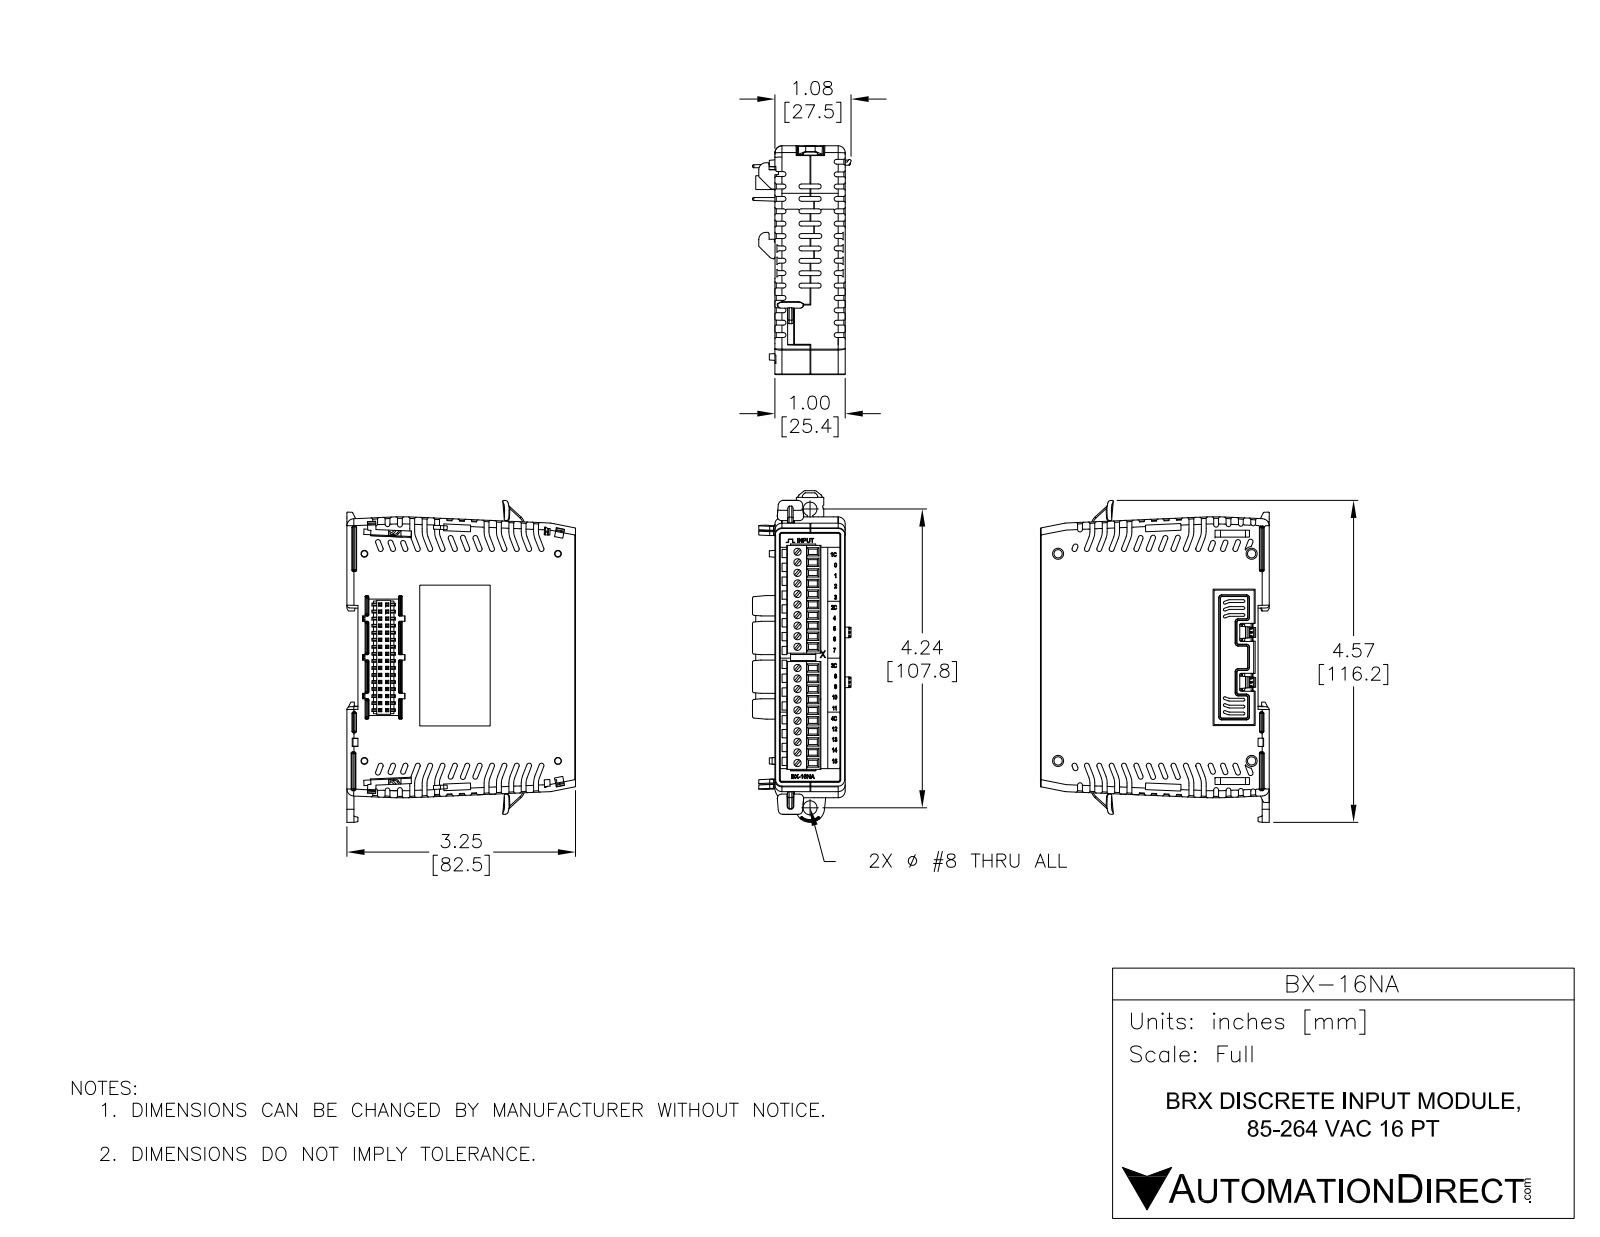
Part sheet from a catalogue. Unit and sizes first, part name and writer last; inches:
Units: inches
Overall size (bounding box): 4.586 × 3.25 × 1.402
Round holes (diameter × count): ⌀0.047 ×2, ⌀0.065 ×2, ⌀0.118 ×2, ⌀0.118 ×2, ⌀0.199 ×1
Round bosses / shafts (diameter × count): ⌀0.062 ×2, ⌀0.059 ×2
Partial cylindrical surfaces — rounded edges, fillets, slot ends (radius × count): R0.005 ×102, R0.008 ×101, R0.01 ×47, R0.02 ×34, R0.005 ×24, R0.062 ×20, R0.117 ×14, R0.039 ×13
Main face-to-face distances: 1, 3.211, 3.22, 0.475, 0.039, 0.157, 3.053, 3.063, 0.1, 0.787
Hole centre spacings: 0.1, 0.824, 0.919, 1.3, 2.093, 2.193, 2.585, 2.617
Volume: 11.58 in³ · Surface area: 72.51 in²
Bodies: 12 solids, 4150 faces (2931 planar, 663 cylindrical, 556 other)
Part name (STEP PRODUCT): BX-16NA
STEP written by: SolidWorks 2017 (AUTOMOTIVE_DESIGN)
